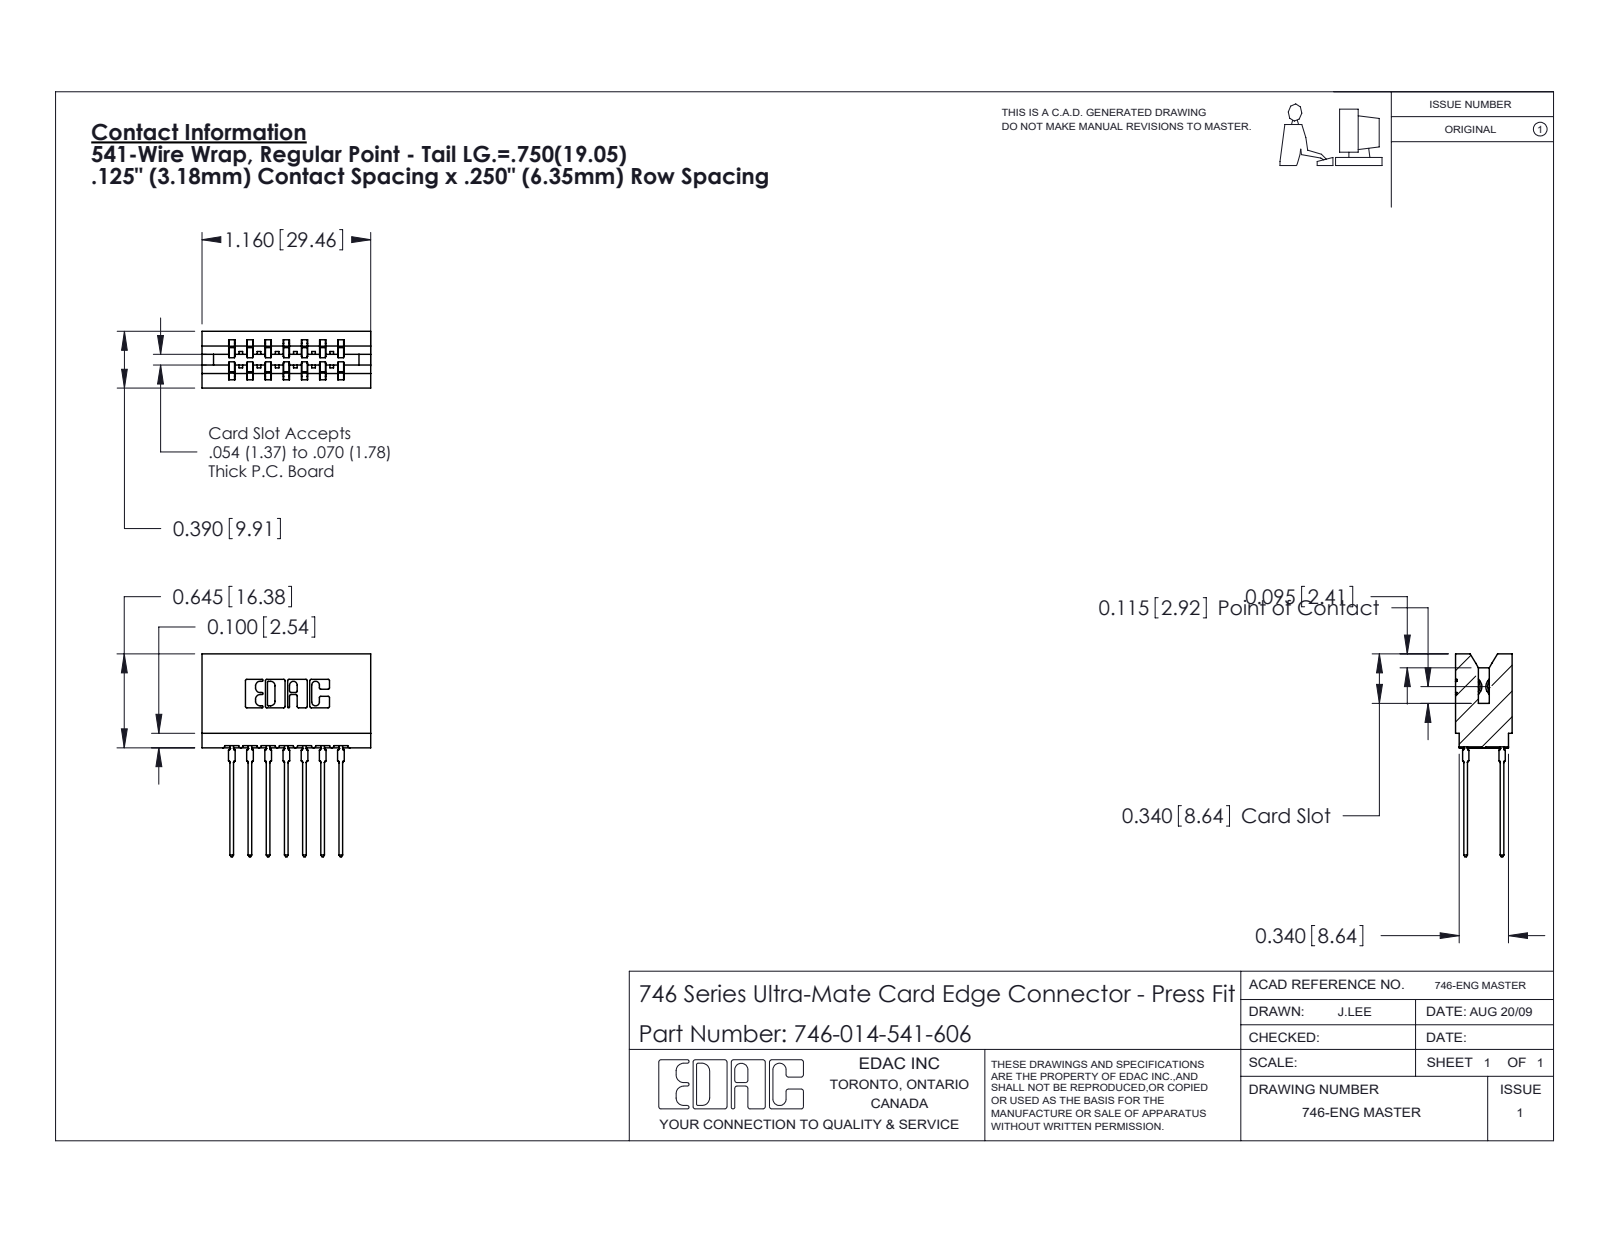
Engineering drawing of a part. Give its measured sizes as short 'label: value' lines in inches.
name: 746-014-541-606; 746-292-001_541; 746 Part_.340 Slot Depth - 06
written by: SolidWorks 2020 (CONFIG_CONTROL_DESIGN)
unit: in
bodies: 15 solids, 1351 faces (700 planar, 287 cylindrical, 364 other)
size: 1.394 × 1.16 × 0.39
volume: 0.222 in³; area: 7.876 in²
rounds: 28× R0.021, 22× R0.01, 8× R0.005, 8× R0.011, 8× R0.015, 6× R0.007, 6× R0.031, 3× R0.026
face distances: 0.25, 0.333, 0.057, 0.042, 0.125, 0.125, 0.083, 0.5, 0.025, 0.292
